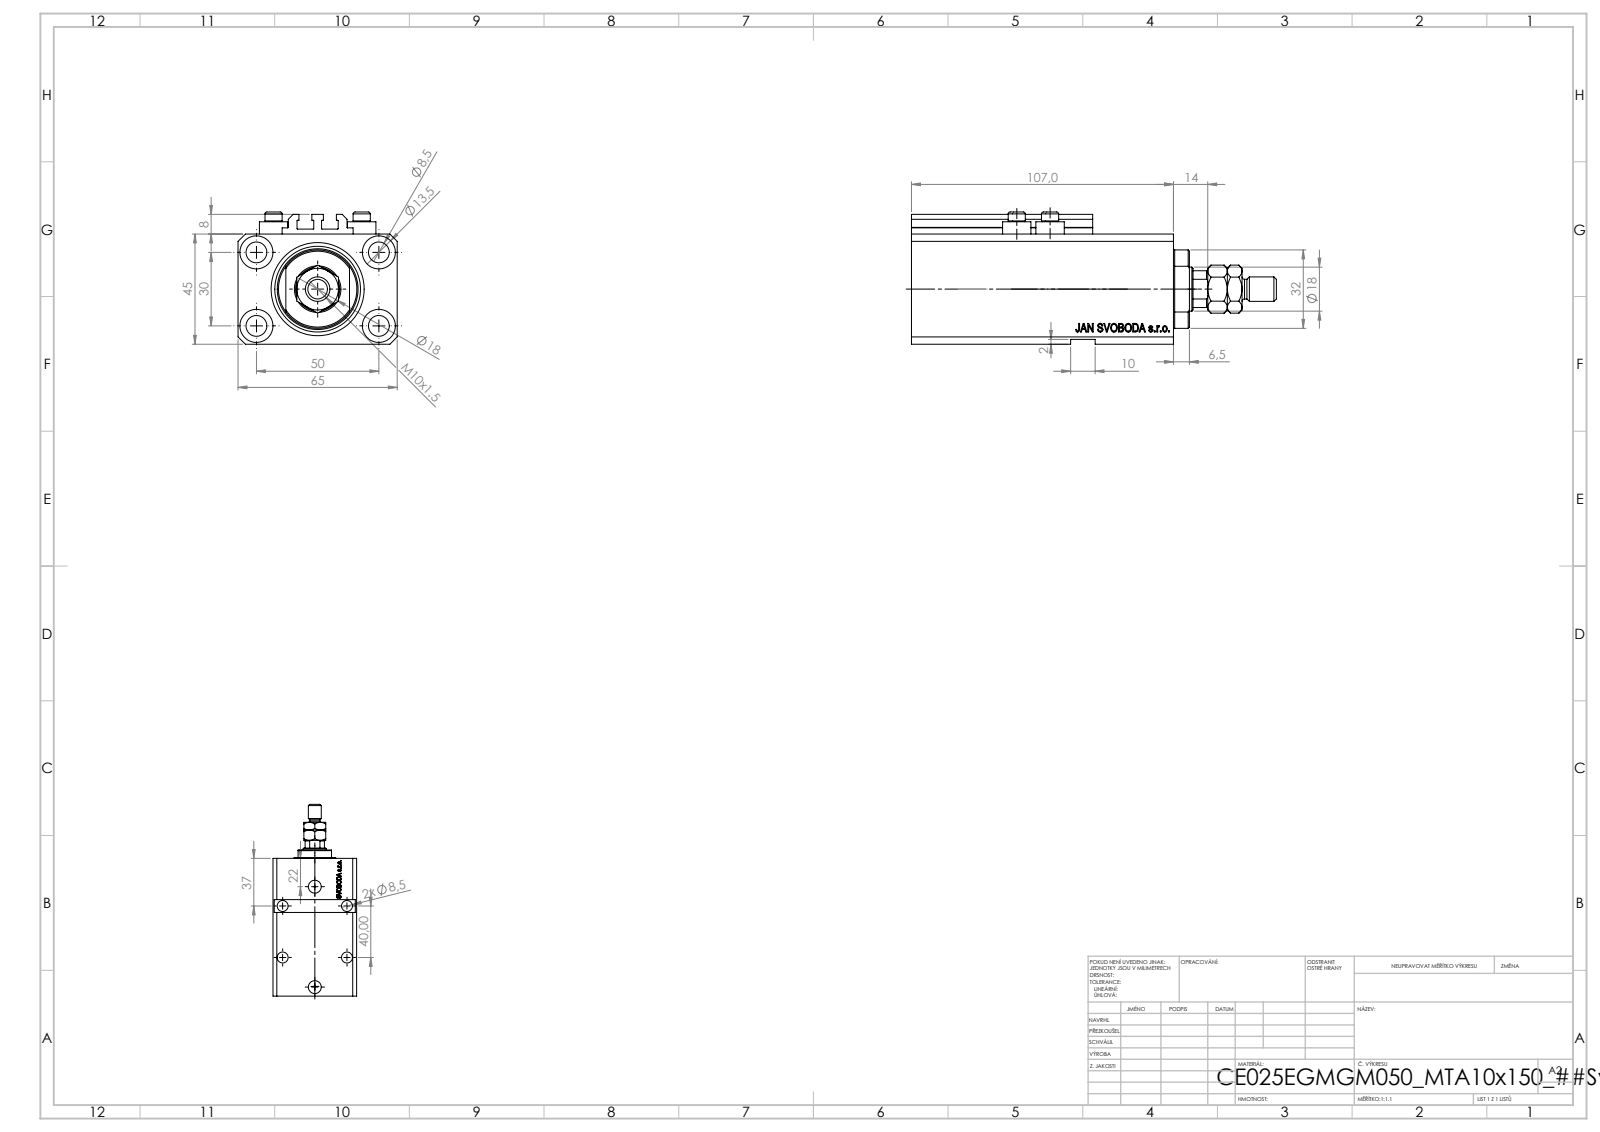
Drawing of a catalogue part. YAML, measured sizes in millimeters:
part_name: "V250CE_E_Body; V250CE_C_VCP; ALLEN BOLT V250CE; MTA (+1 more)"
step_written_by: "SolidWorks 2019 (CONFIG_CONTROL_DESIGN)"
units: millimeters
bodies: {solids: 9, faces: 1136, planar: 526, cylindrical: 150, other: 460}
overall_size: [149, 65, 54]
volume: 277886
surface_area: 78614
round_holes:
  - {diameter: 8.5, count: 9}
  - {diameter: 1.25, count: 4}
  - {diameter: 4, count: 4}
  - {diameter: 13.5, count: 4}
  - {diameter: 10, count: 2}
  - {diameter: 13.16, count: 2}
  - {diameter: 20, count: 2}
  - {diameter: 18, count: 1}
  - {diameter: 25, count: 1}
  - {diameter: 38, count: 1}
round_bosses_or_shafts:
  - {diameter: 11.6, count: 4}
  - {diameter: 7, count: 4}
  - {diameter: 10, count: 1}
  - {diameter: 8, count: 1}
partial_cylinders:
  - {radius: 0.2, count: 10}
  - {radius: 8.5, count: 1}
  - {radius: 16, count: 1}
face_to_face_distances: [45, 65, 14, 93, 2, 47, 107, 6.9, 20.5, 2.5]
hole_center_spacings: [29.15, 50, 13.6, 14.76, 15.12, 27.51, 27.89, 30]
